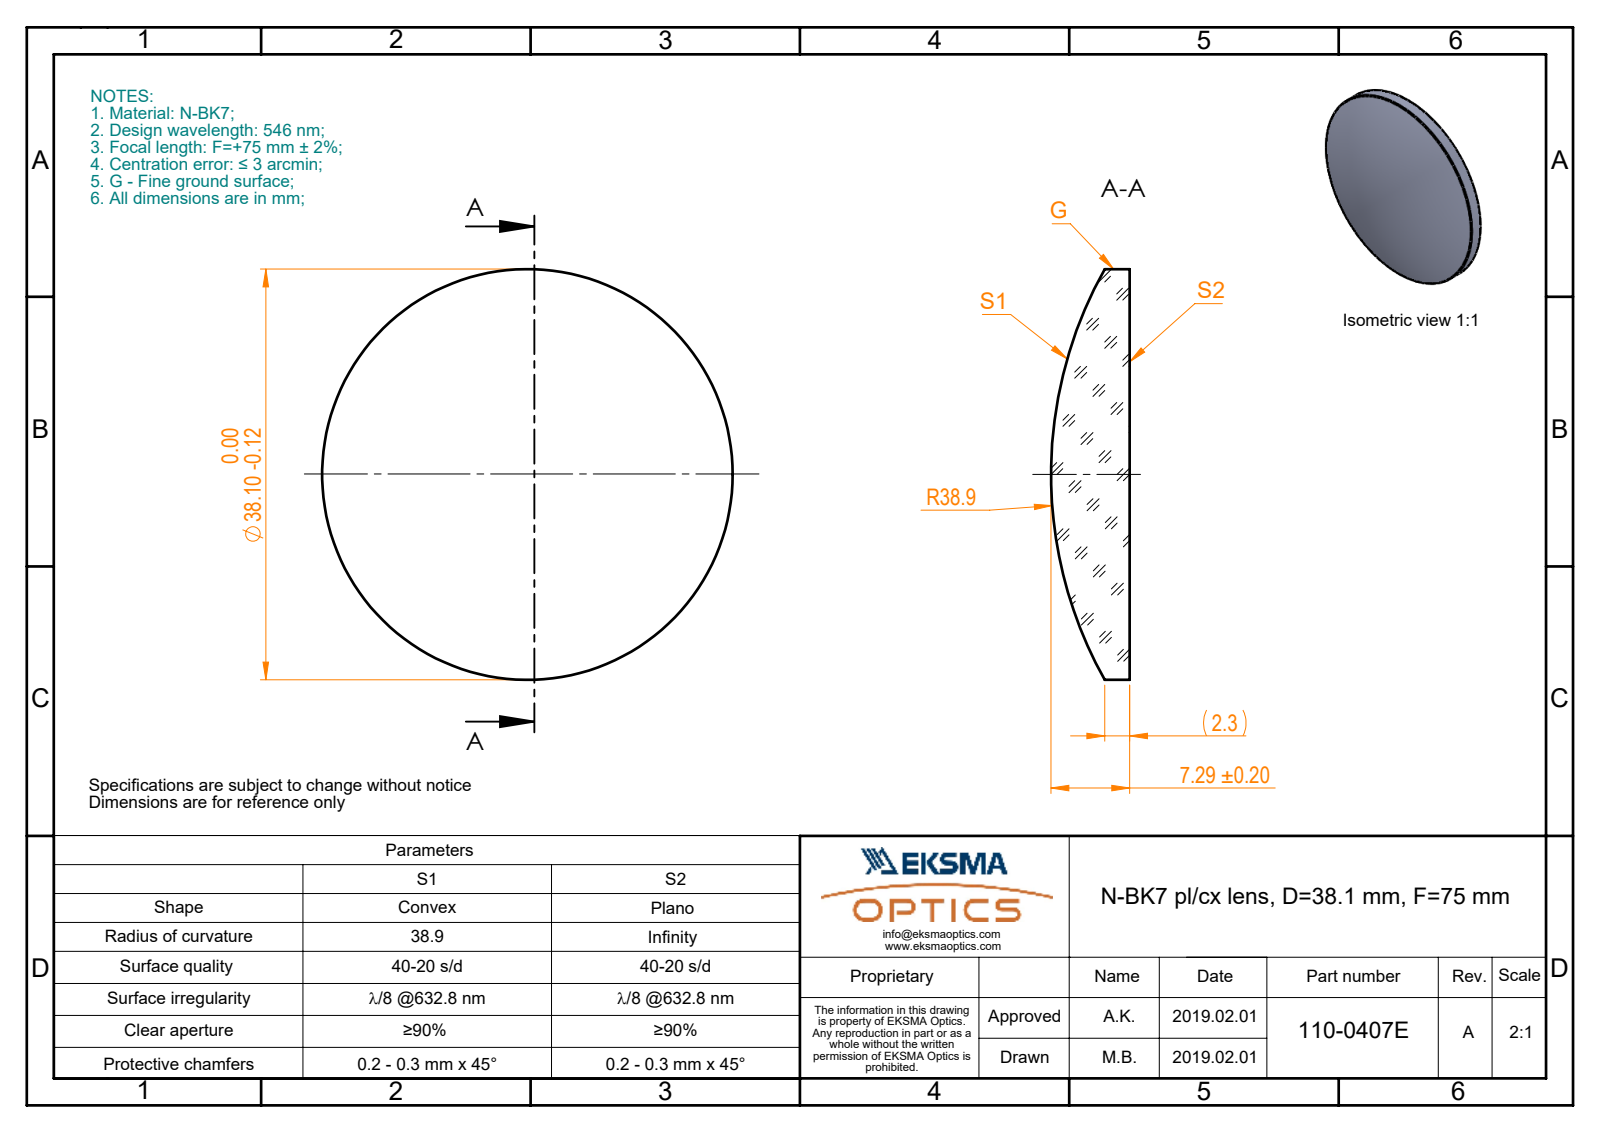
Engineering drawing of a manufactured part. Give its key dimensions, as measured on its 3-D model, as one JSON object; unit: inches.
{"part_name": "110-0407E BK7 pl-cx 38.1 F75", "step_written_by": "SolidWorks 2017 (CONFIG_CONTROL_DESIGN)", "units": "inches", "bodies": {"solids": 1, "faces": 5, "planar": 1, "cylindrical": 2, "other": 2}, "overall_size": [1.5, 1.5, 0.287], "volume_in3": 0.338, "surface_area_in2": 4.084, "round_bosses_or_shafts": [[1.5, 1]]}
